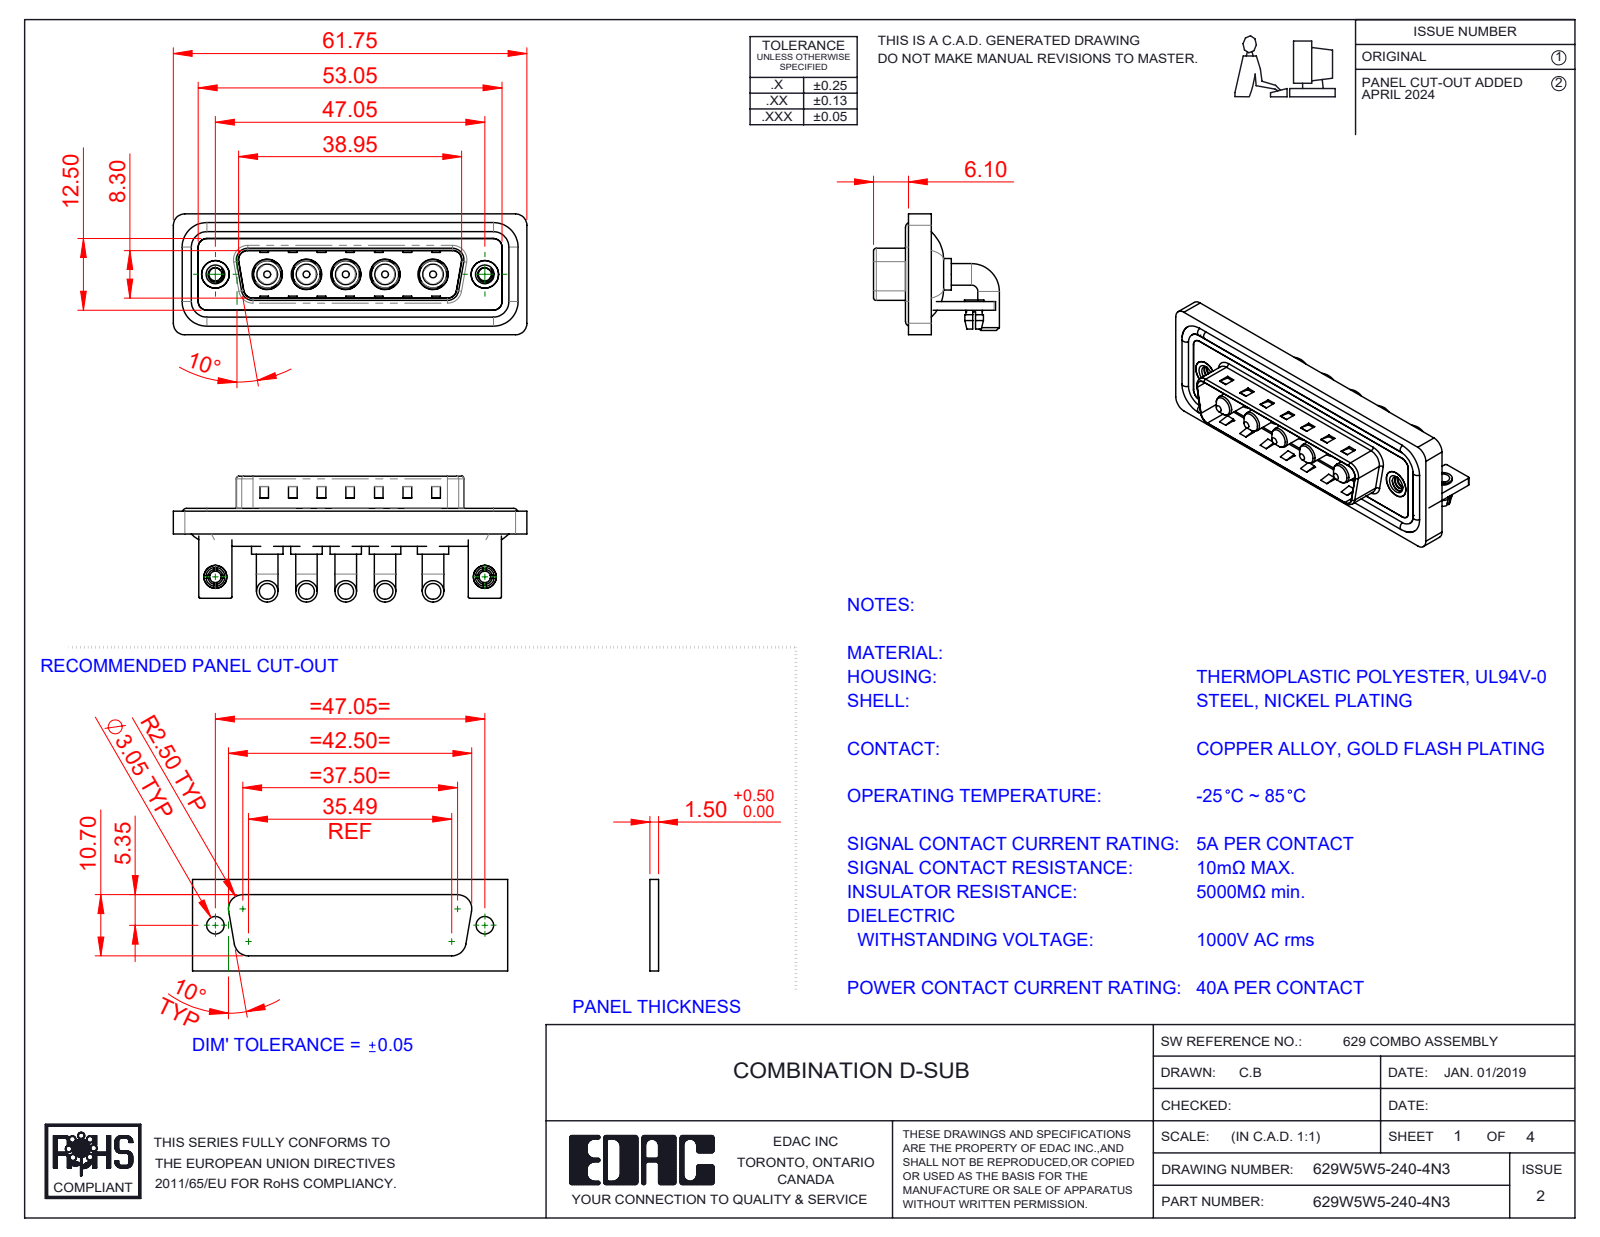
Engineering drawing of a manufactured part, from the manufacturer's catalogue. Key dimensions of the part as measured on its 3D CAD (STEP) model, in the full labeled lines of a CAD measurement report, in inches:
Part name (STEP PRODUCT): 629Combo Threaded Rivet_3; 629Combo Stabilizer Bracket; Power Pin_40A RA; 629Combo Shell Front_25 Contacts (+5 more)
STEP written by: SolidWorks 2023 (CONFIG_CONTROL_DESIGN)
Units: inches
Bodies: 21 solids, 830 faces (327 planar, 343 cylindrical, 160 other)
Overall size (bounding box): 2.431 × 0.865 × 0.831
Volume: 0.517 in³ · Surface area: 20.6 in²
Round holes (diameter × count): ⌀0.191 ×5, ⌀0.209 ×5, ⌀0.079 ×2, ⌀0.089 ×2, ⌀0.098 ×2, ⌀0.126 ×2, ⌀0.157 ×2, ⌀0.189 ×2, ⌀0.197 ×2
Round bosses / shafts (diameter × count): ⌀0.148 ×10, ⌀0.217 ×5, ⌀0.205 ×5, ⌀0.187 ×5, ⌀0.142 ×5, ⌀0.063 ×4, ⌀0.193 ×2, ⌀0.157 ×2
Partial cylindrical surfaces — rounded edges, fillets, slot ends (radius × count): R0.079 ×19, R0.059 ×18, R0.01 ×16, R0.02 ×9, R0.063 ×8, R0.083 ×5, R0.024 ×4, R0.026 ×4
Main face-to-face distances: 0.016, 0.059, 0.114, 0.031, 0.083, 0.043, 0.146, 0.177, 0.161, 0.047
Hole centre spacings: 0.27, 0.541, 1.852, 0.27, 0.27, 0.33, 0.33, 0.356
